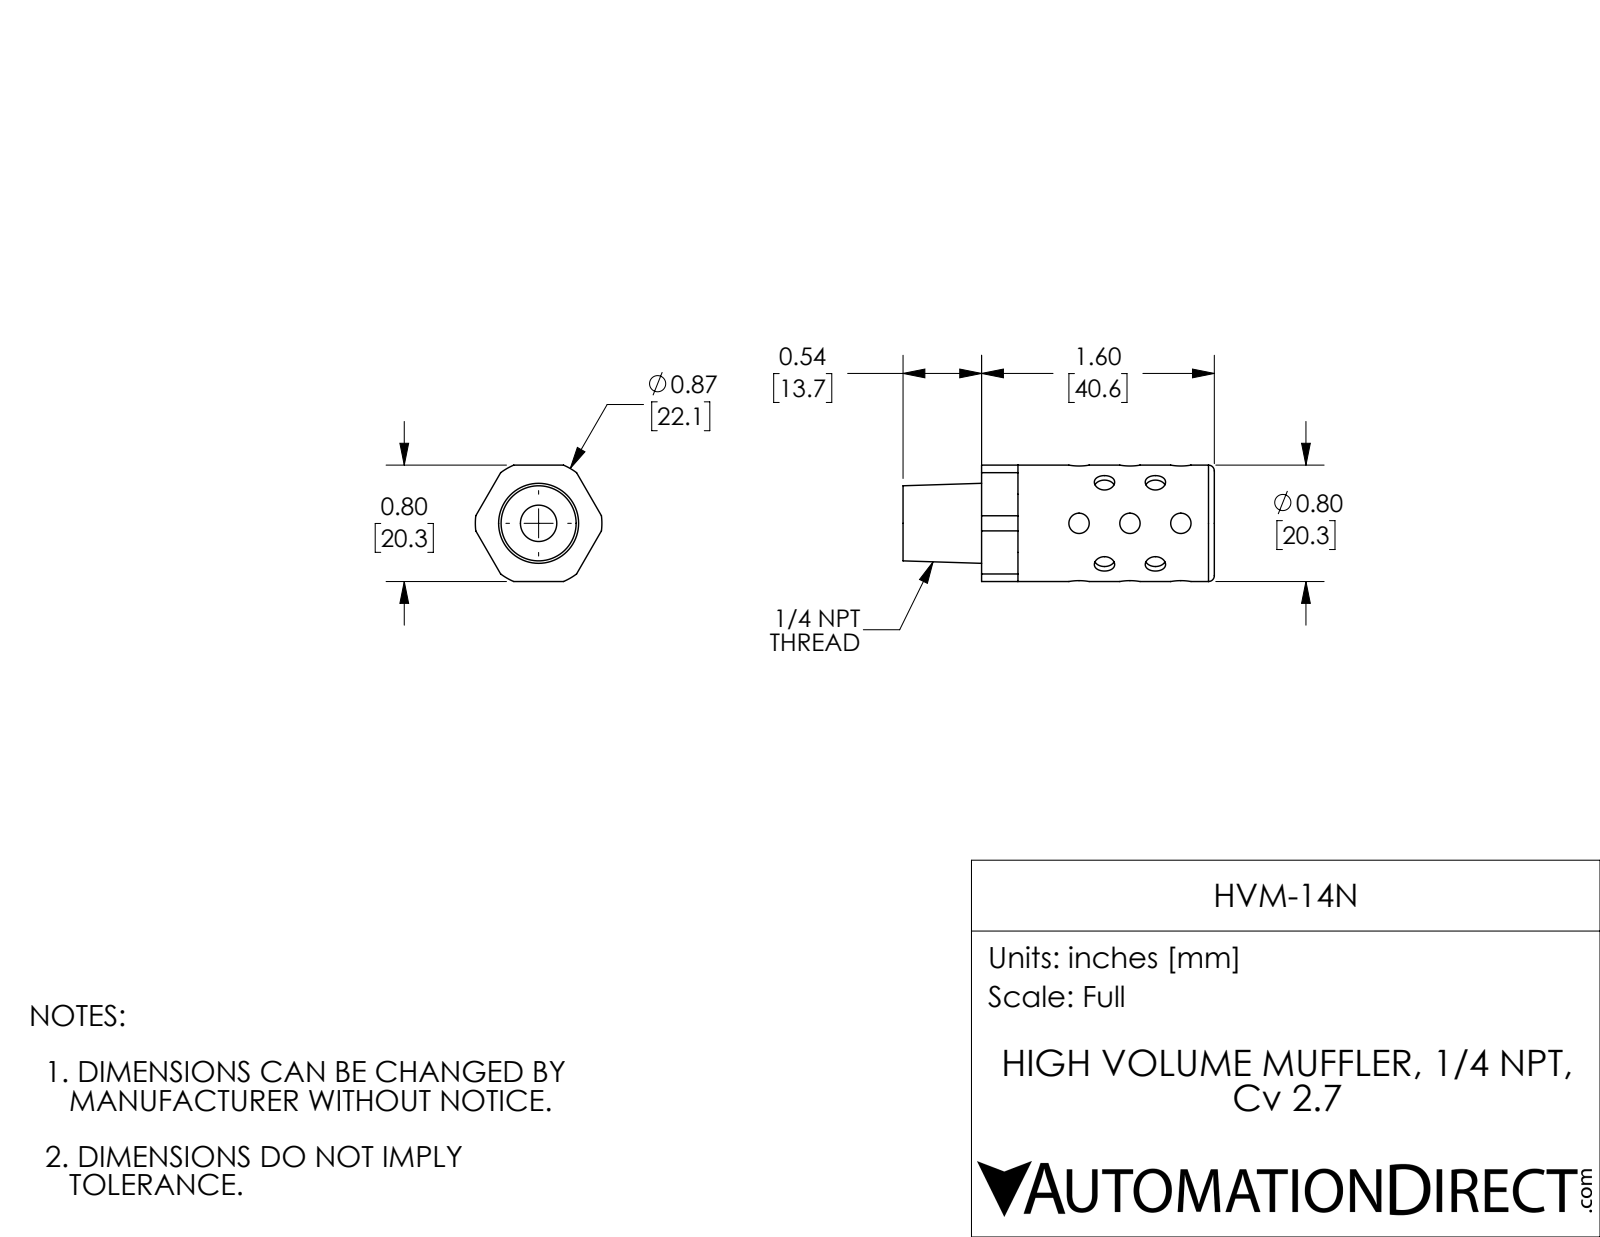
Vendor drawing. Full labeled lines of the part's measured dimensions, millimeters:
Part name (STEP PRODUCT): HVM-14N
STEP written by: SolidWorks 2017 (AUTOMOTIVE_DESIGN)
Units: millimetres
Bodies: 1 solid, 91 faces (36 planar, 51 cylindrical, 4 other)
Overall size (bounding box): 54.4 × 22.1 × 20.3
Volume: 13 600 mm³ · Surface area: 5 086 mm²
Round holes (diameter × count): ⌀3.6 ×10, ⌀6.4 ×1
Round bosses / shafts (diameter × count): ⌀20.3 ×1
Partial cylindrical surfaces — rounded edges, fillets, slot ends (radius × count): R11 ×1
Main face-to-face distances: 40.6, 20.3, 13.7, 54.4, 17.8, 6.4, 34.3, 1.3, 19.1, 48
Hole centre spacings: 8.9, 17.8
